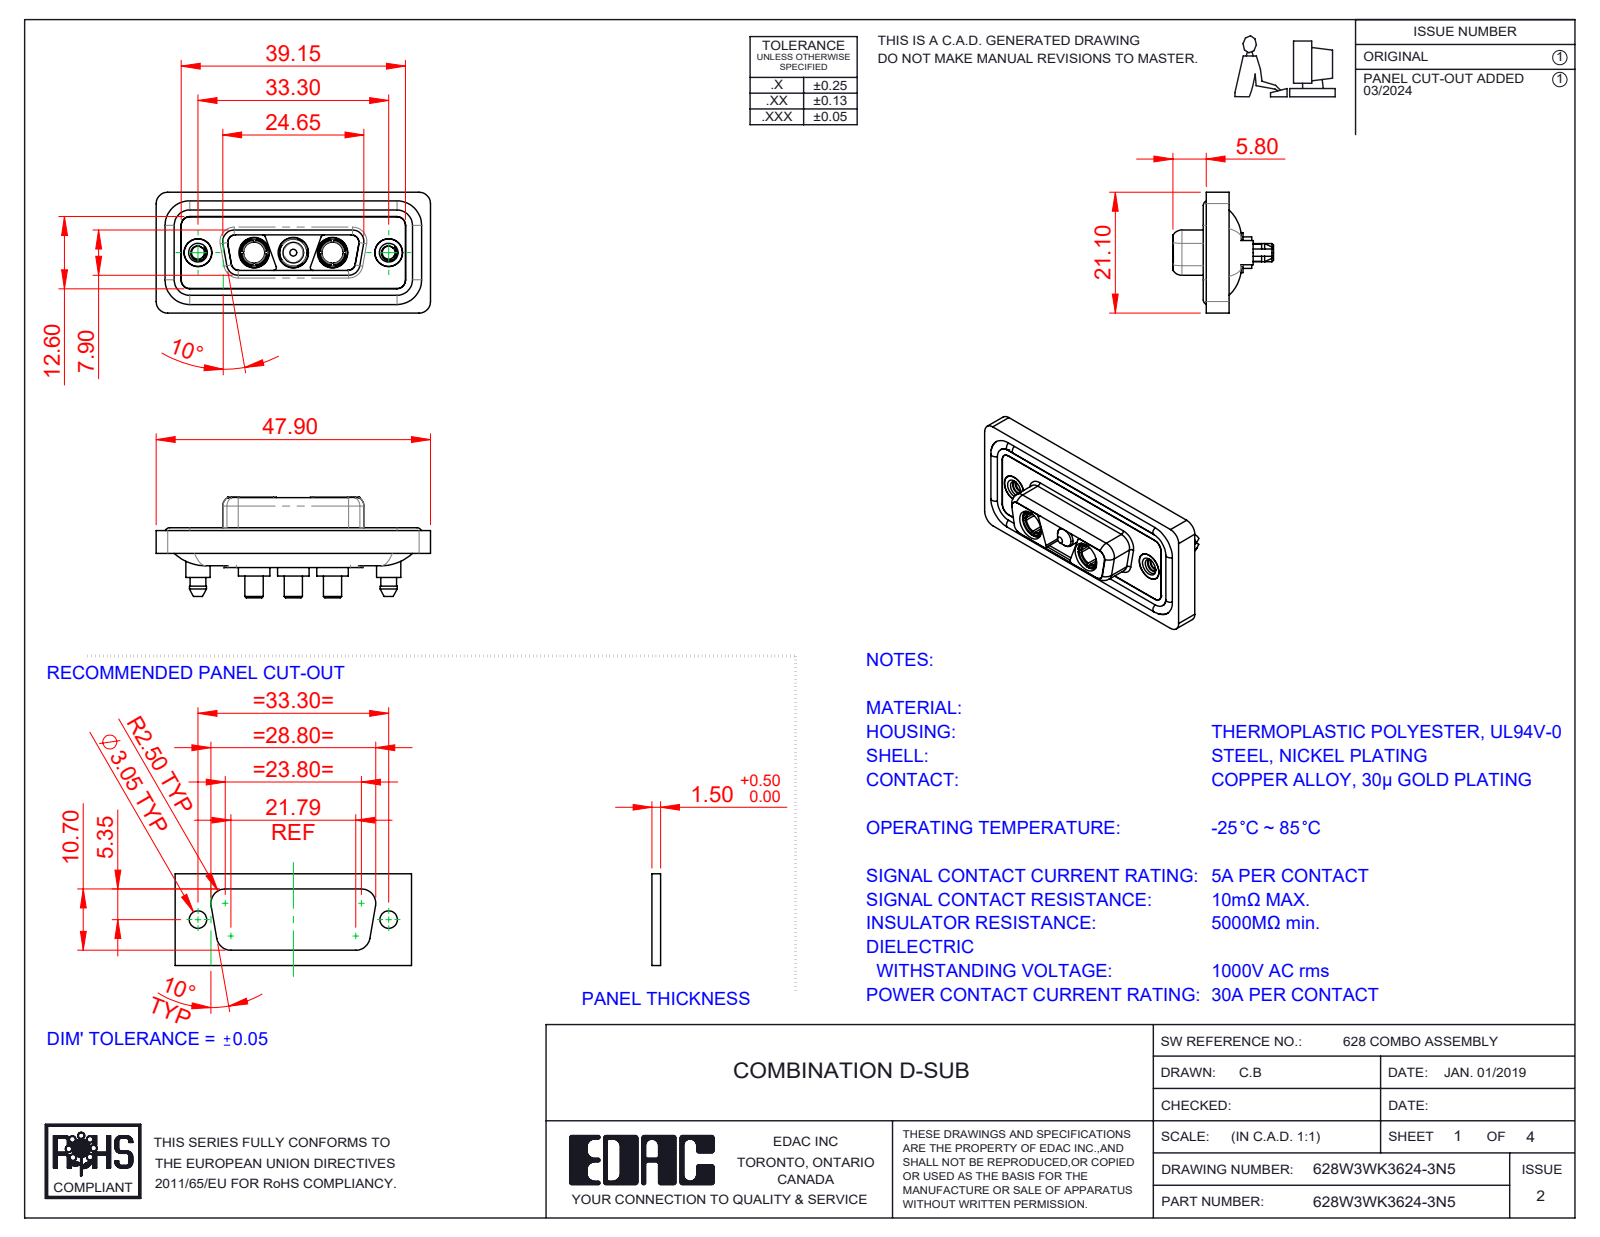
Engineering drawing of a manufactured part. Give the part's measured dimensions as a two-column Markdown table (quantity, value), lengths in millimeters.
| quantity | value |
| --- | --- |
| part name | 628W3WK3624-3N5; 628Combo Waterproof Housing_15 Contacts; Power Socket_30A S; 628Combo Shell Front_15 Contacts (+4 more) |
| STEP written by | SolidWorks 2023 (CONFIG_CONTROL_DESIGN) |
| units | millimeters |
| bodies | 13 solids, 633 faces (194 planar, 290 cylindrical, 149 other) |
| overall size | 47.9 × 21.1 × 17.55 |
| volume | 6 033 mm³ |
| surface area | 9 852 mm² |
| round holes (diameter × count) | 4.85 × 5, 5.3 × 3, 2.26 × 2, 3.7 × 2, 4 × 2, 4.05 × 2, 5 × 2 |
| round bosses / shafts (diameter × count) | 1.6 × 4, 5.5 × 3, 5.2 × 3, 4.75 × 3, 3.75 × 3, 3.2 × 3, 5.4 × 2, 4.96 × 2 |
| partial cylindrical surfaces (radius × count) | 1.5 × 24, 2 × 20, 1.35 × 12, 1.6 × 10, 0.5 × 8, 0.25 × 4, 0.6 × 4, 0.65 × 4 |
| main face-to-face distances | 0.4, 1.6, 1.8, 0.5, 1.1, 2.9, 5.65, 7.05, 1.5, 5.35 |
| hole center spacings | 6.85, 9.8, 16.65, 23.5, 13.7, 33.3 |
